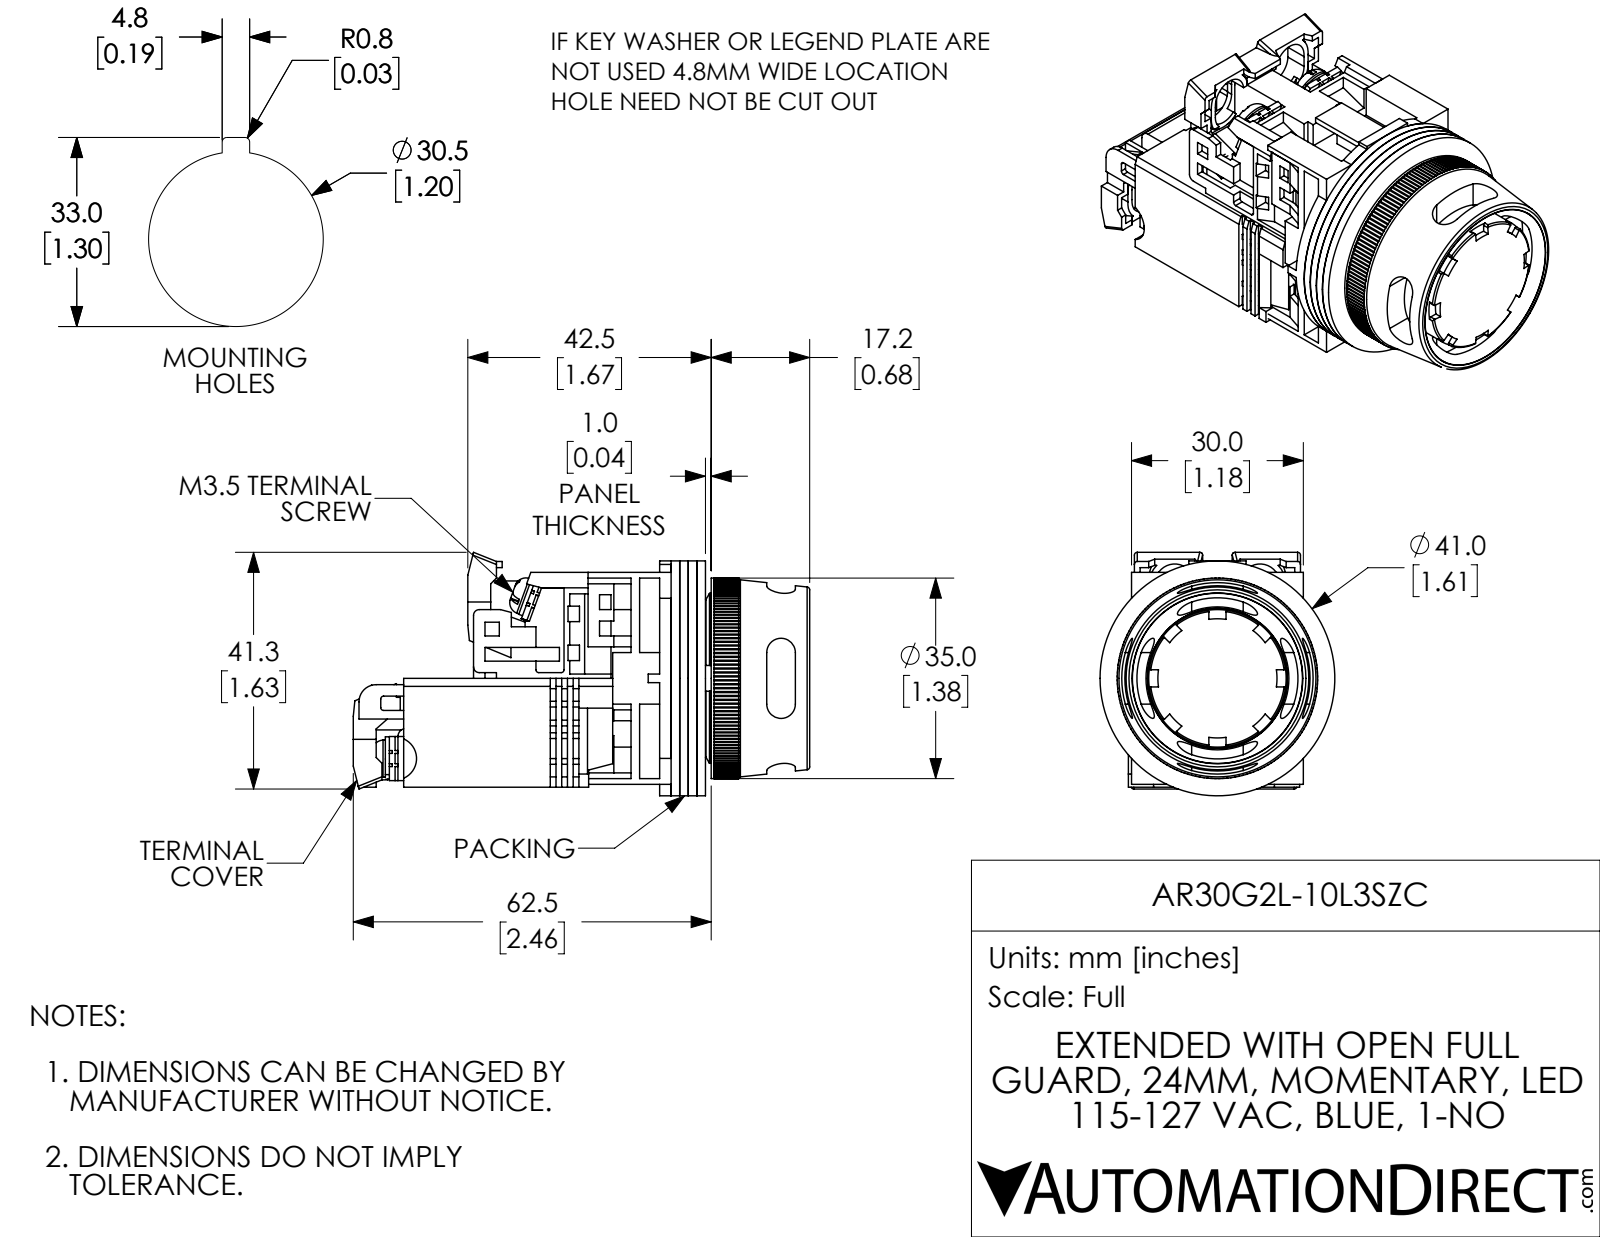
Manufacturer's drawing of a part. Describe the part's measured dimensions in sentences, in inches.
The part is named "AR30G2L-10L3SZC". Its 3-D file was written by "SolidWorks 2017 (AUTOMOTIVE_DESIGN)". It is 27 solids with 2102 faces: 1483 planar, 474 cylindrical and 145 other. Overall it measures 3.138 by 1.673 by 1.614 inches. Its volume is 2.906 cubic inches and its surface area 66.69 square inches. Round holes: 6 of diameter 0.138, 4 of diameter 0.142, 3 of diameter 0.118, 1 of diameter 0.472, 1 of diameter 0.709, 1 of diameter 0.728, 1 of diameter 0.787, 1 of diameter 0.945, 1 of diameter 1.252. Round bosses or shafts: 4 of diameter 0.26, 2 of diameter 0.138, 1 of diameter 1.614, 1 of diameter 1.378, 1 of diameter 1.181, 1 of diameter 0.866, 1 of diameter 0.776, 1 of diameter 0.551. Partial cylindrical surfaces (rounded edges, fillets, slot ends): 160 of radius 0.01, 17 of radius 0.059, 16 of radius 0.012, 13 of radius 0.02, 4 of radius 0.098, 4 of radius 0.138, 4 of radius 0.177, 2 of radius 0.039. The main face-to-face distances are 0.059, 0.118, 0.177, 0.039, 0.748, 0.276, 0.079, 1.417, 0.689, 0.138. The hole center spacings are 0.579, 0.02, 0.274, 0.32, 0.325, 0.583, 0.583, 0.61.
